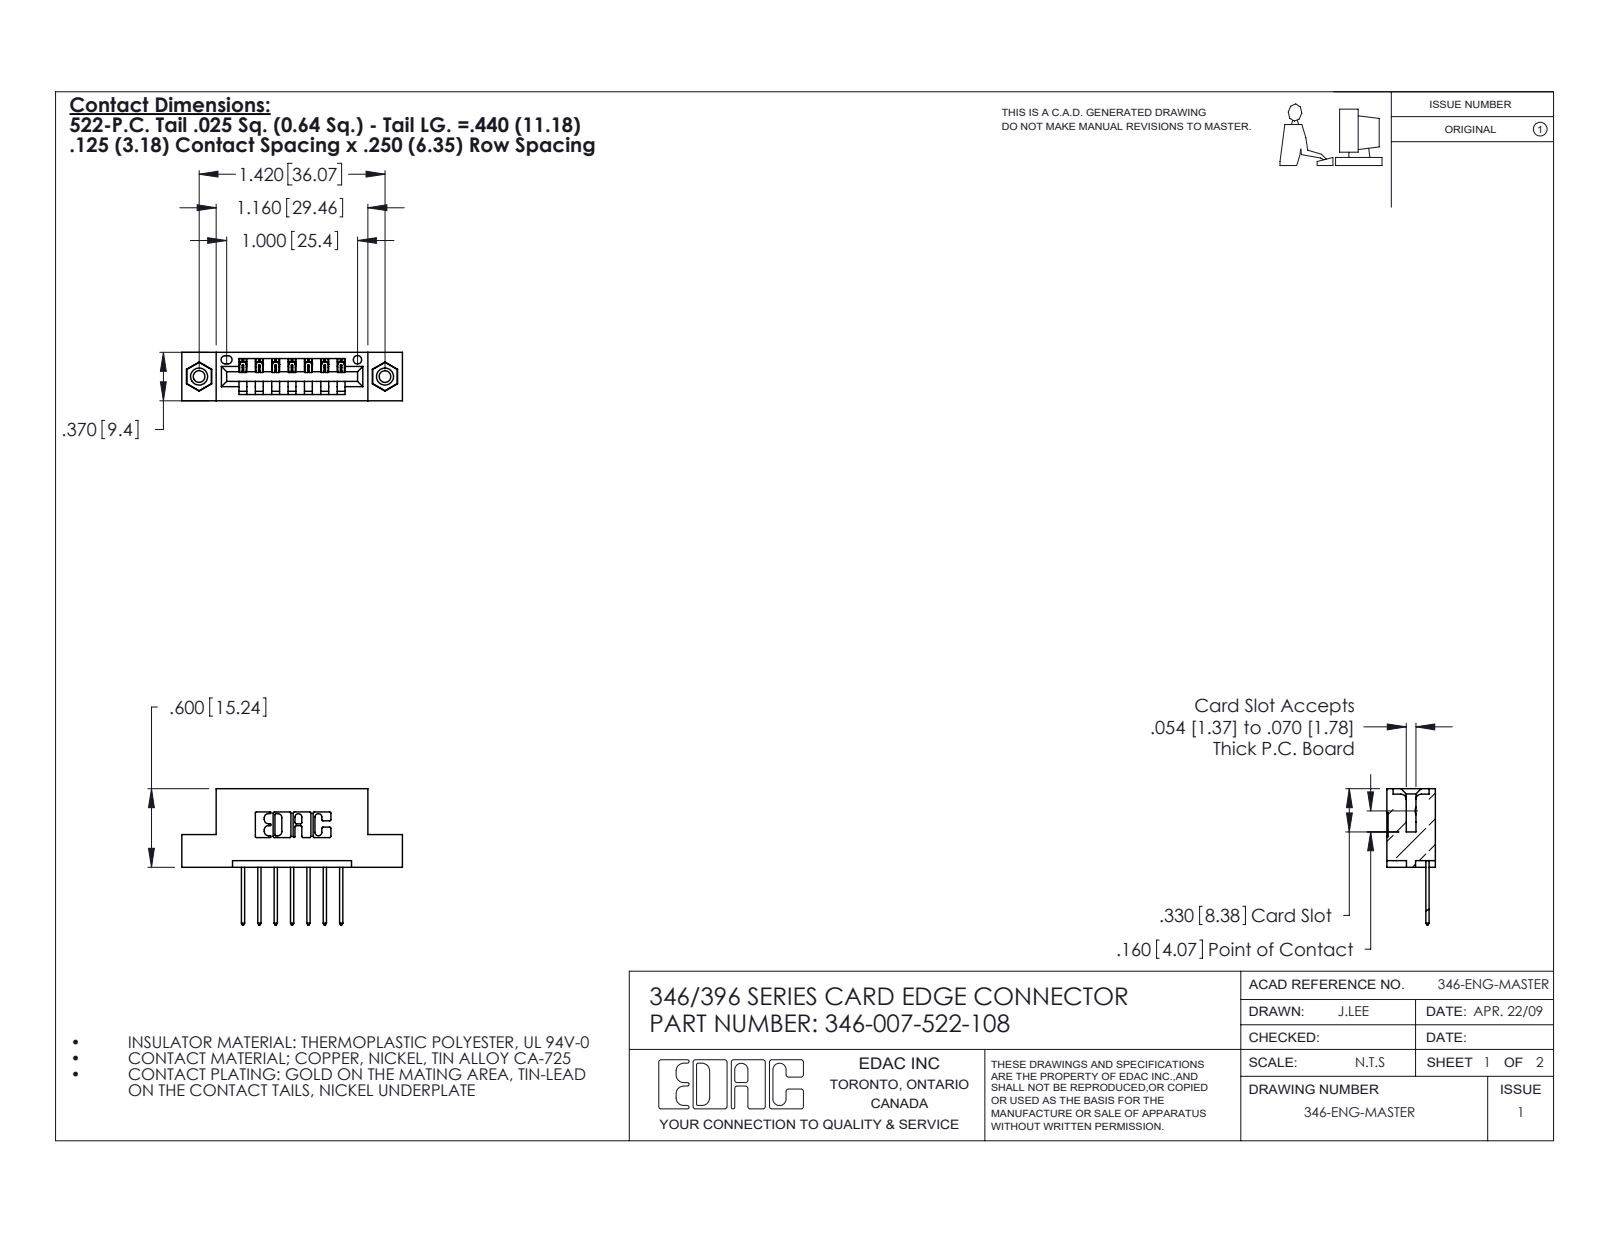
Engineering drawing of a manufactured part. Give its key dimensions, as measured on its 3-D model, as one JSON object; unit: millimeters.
{"part_name": "345-292-001_345-293-122; 345-250-001_345-250-003-102; 346 Part_Flush Mounting Lugs - 0.156 Dia-TI; 346-007-522-108", "step_written_by": "SolidWorks 2020 (CONFIG_CONTROL_DESIGN)", "units": "millimeters", "bodies": {"solids": 10, "faces": 588, "planar": 388, "cylindrical": 184, "other": 16}, "overall_size": [42.8, 26.4, 9.4], "volume_mm3": 3850, "surface_area_mm2": 4482, "round_holes": [[2.3, 2], [3.2, 2], [4, 2], [1.6, 1]], "round_bosses_or_shafts": [[3.9, 2]], "partial_cylinders_radius": [[0.3, 22], [0.2, 14], [0.3, 14], [0.2, 6], [0.8, 6], [0.7, 3], [0.8, 2], [1, 2]], "face_to_face_distances": [6.4, 9.4, 1.2, 8.2, 1.8, 7.6, 0.6, 3.8, 5.6, 2.5], "hole_center_spacings": [6.2, 30.9, 36.1]}
